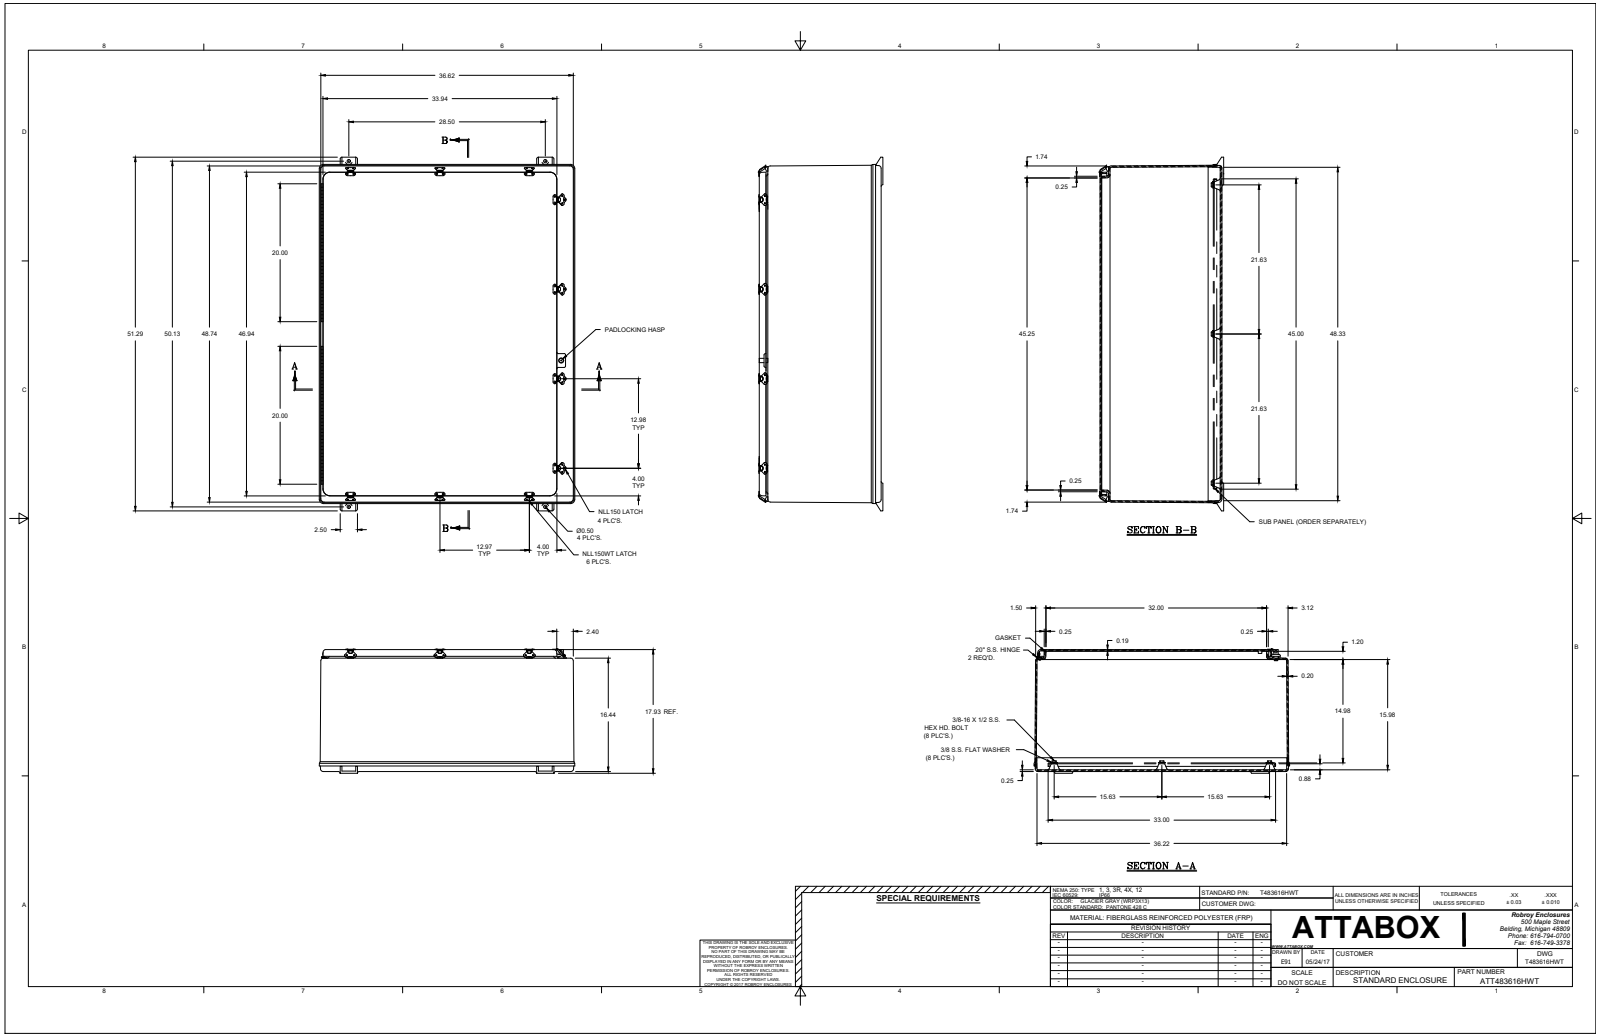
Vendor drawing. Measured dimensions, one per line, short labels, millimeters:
name: T483616HWT
written by: SolidWorks 2018 (AUTOMOTIVE_DESIGN)
unit: mm
bodies: 121 solids, 3002 faces (1131 planar, 1226 cylindrical, 645 other)
size: 1302.5 × 941.4 × 463.7
volume: 23 930 000 mm³; area: 9 198 000 mm²
holes: 76× ⌀3.3, 40× ⌀1.6, 20× ⌀3.5, 20× ⌀4.7, 8× ⌀1.7, 8× ⌀1.7, 8× ⌀14.3, 3× ⌀3.4, 3× ⌀4, 2× ⌀3.7, 2× ⌀7.1, 2× ⌀13
bosses: 40× ⌀3.6, 16× ⌀7.5, 10× ⌀12.7, 3× ⌀5.1, 1× ⌀6.4, 1× ⌀5.1, 1× ⌀3.4
rounds: 217× R0.3, 40× R0.8, 33× R7.9, 24× R6.4, 20× R5.3, 20× R30.1, 18× R9.5, 12× R1.6
face distances: 5.2, 6.4, 4.8, 448.9, 442.5, 444.1, 437.8, 417.9, 31, 412.8
hole spacings: 312.8, 25.4, 158.8, 161.9, 161.9, 277.8, 320.7, 320.7
